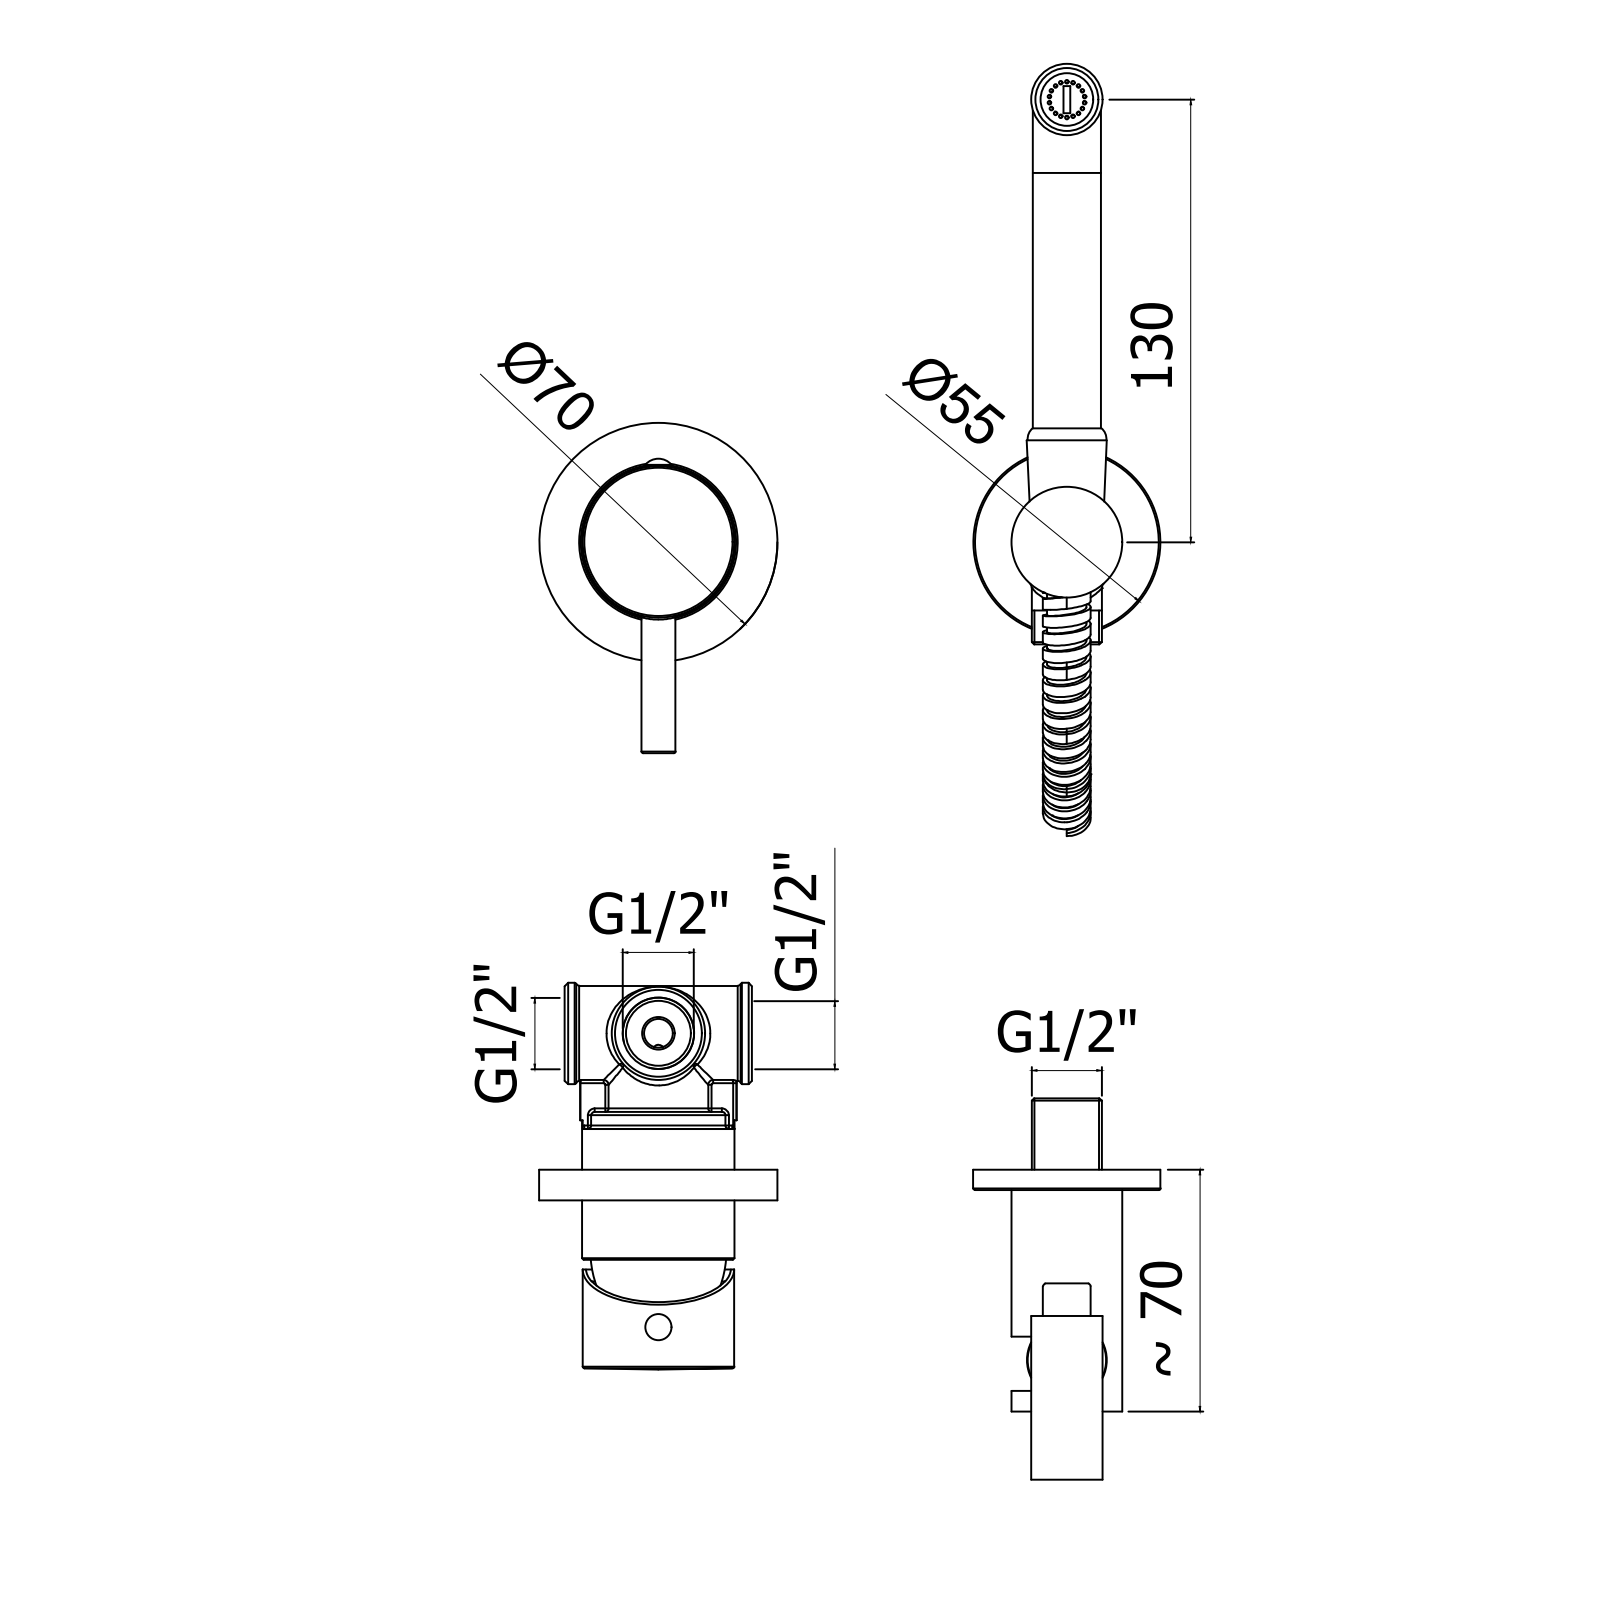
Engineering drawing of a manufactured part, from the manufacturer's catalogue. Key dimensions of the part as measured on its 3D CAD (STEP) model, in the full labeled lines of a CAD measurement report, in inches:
Part name (STEP PRODUCT): KITDUP110CR
STEP written by: CREO PARAMETRIC BY PTC INC, 2020044 (CONFIG_CONTROL_DESIGN)
Units: inches
Bodies: 4 solids, 1369 faces (659 planar, 378 cylindrical, 332 other)
Overall size (bounding box): 8.929 × 7.185 × 3.583
Volume: 7.963 in³ · Surface area: 160.1 in²
Round holes (diameter × count): ⌀0.039 ×18, ⌀0.157 ×2, ⌀0.197 ×2, ⌀0.512 ×2, ⌀0.551 ×2, ⌀0.591 ×2, ⌀0.728 ×2, ⌀0.083 ×1, ⌀0.118 ×1, ⌀0.13 ×1, ⌀0.224 ×1, ⌀0.335 ×1
Round bosses / shafts (diameter × count): ⌀0.827 ×2, ⌀0.811 ×2, ⌀0.787 ×2, ⌀0.669 ×2, ⌀2.756 ×1, ⌀2.165 ×1, ⌀2.15 ×1, ⌀1.764 ×1
Partial cylindrical surfaces — rounded edges, fillets, slot ends (radius × count): R0.02 ×34, R0.006 ×11, R0.012 ×4, R0.039 ×2, R0.276 ×2, R0.175 ×1, R0.222 ×1, R0.315 ×1
Main face-to-face distances: 0.177, 0.059, 0.118, 0.354, 0.236, 0.079, 0.098, 0.039, 0.295, 0.217
Hole centre spacings: 0.207, 0.407, 0.141, 0.317, 0.358, 0.388, 0.072, 0.265
